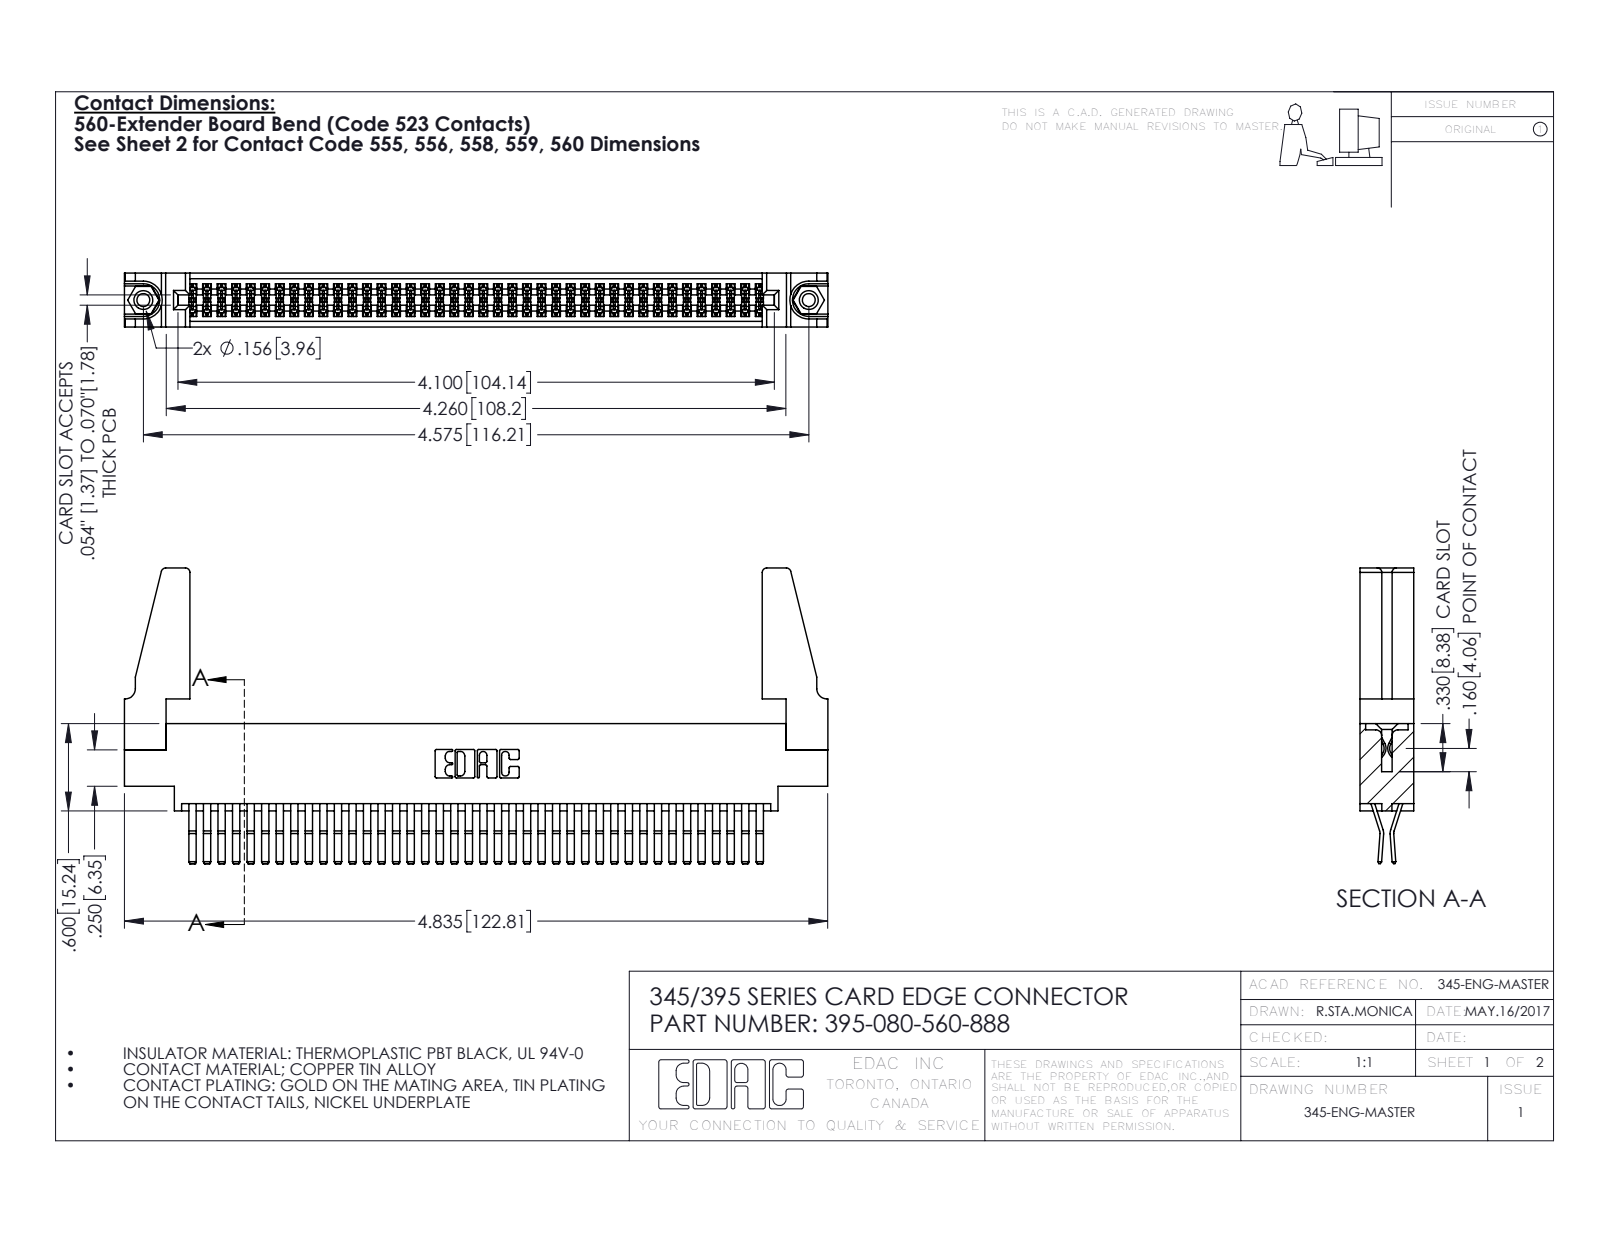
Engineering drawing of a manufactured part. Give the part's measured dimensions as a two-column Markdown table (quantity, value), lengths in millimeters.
| quantity | value |
| --- | --- |
| part name | 345-220-078_345-220-088; 345-292-001_560 Tail; 345 Part_0.170 Offset - 0.156 Dia-TH; 395-080-560-888 (+1 more) |
| STEP written by | SolidWorks 2016 (CONFIG_CONTROL_DESIGN) |
| units | millimeters |
| bodies | 85 solids, 4414 faces (2796 planar, 1602 cylindrical, 16 other) |
| overall size | 122.8 × 51.6 × 9.4 |
| volume | 15 600 mm³ |
| surface area | 22 790 mm² |
| round holes (diameter × count) | 2.3 × 2, 3.2 × 2, 4 × 2, 1.6 × 1 |
| round bosses / shafts (diameter × count) | 3.9 × 2 |
| partial cylindrical surfaces (radius × count) | 0.2 × 121, 0.3 × 22, 0.8 × 8, 0.2 × 6, 0.8 × 6, 0.7 × 3, 0.3 × 2, 0.4 × 2 |
| main face-to-face distances | 1.8, 7.6, 0.6, 9.4, 5.1, 2.5, 6.9, 5.7, 4.4, 3.8 |
| hole center spacings | 6.9, 110.2, 116.2 |
